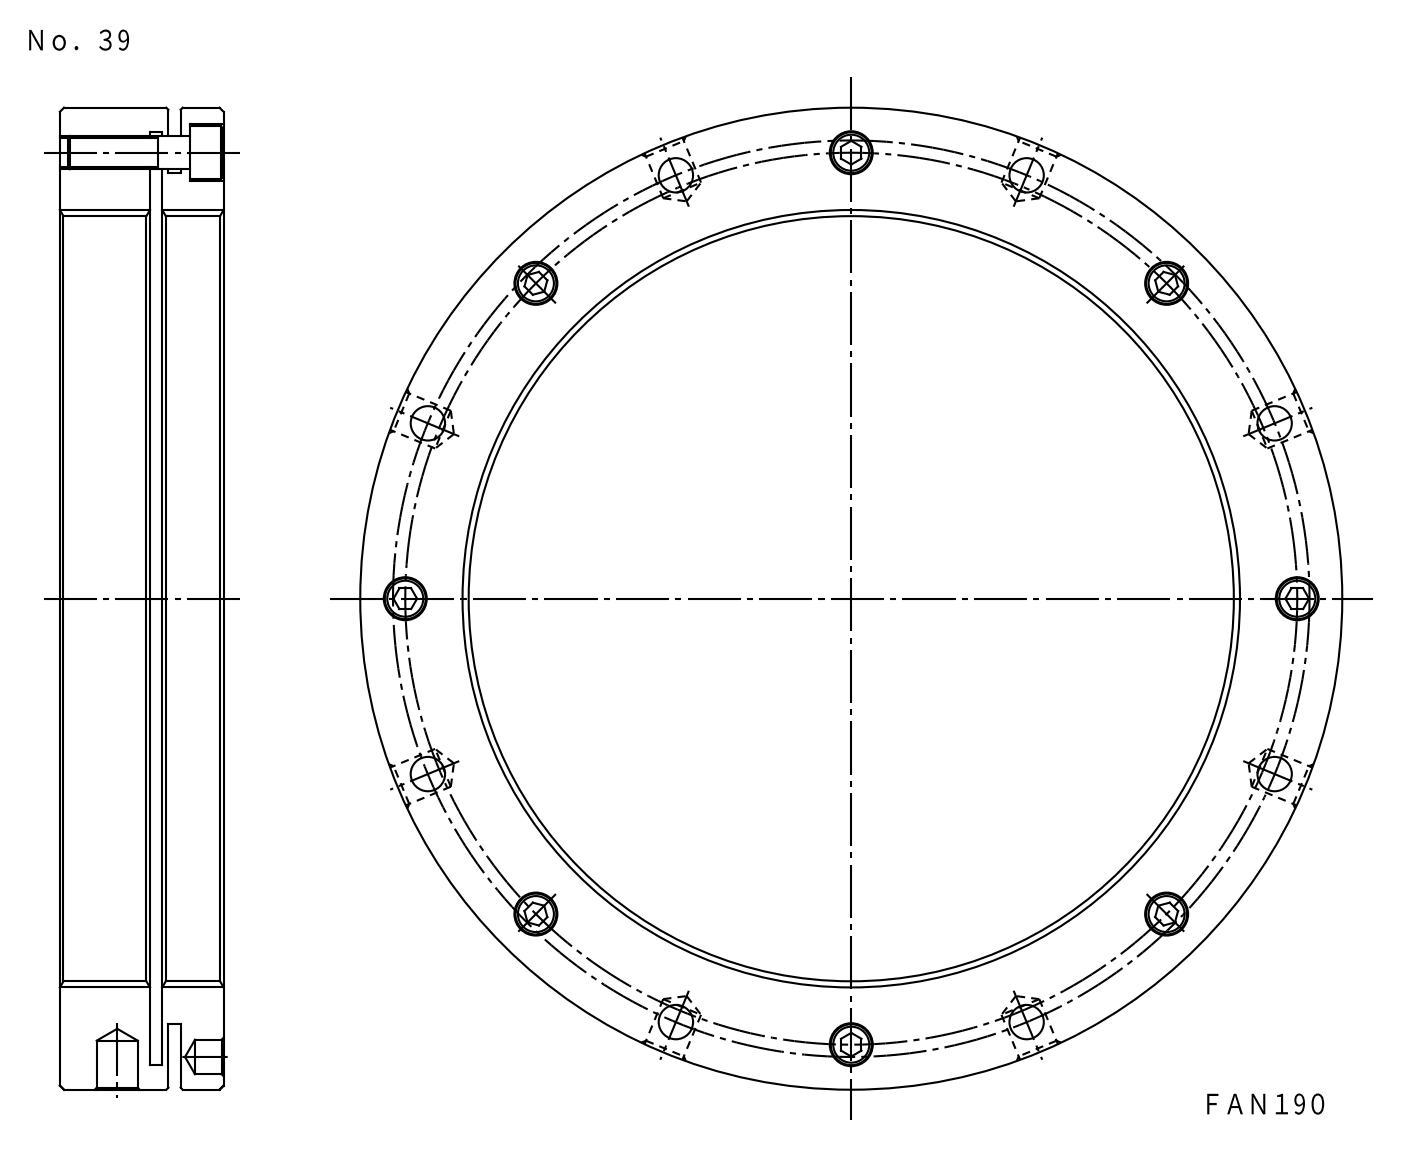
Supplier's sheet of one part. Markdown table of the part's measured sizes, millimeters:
| quantity | value |
| --- | --- |
| part name | FKD FAN190; M8X30_default |
| STEP written by | SolidWorks 2012 (CONFIG_CONTROL_DESIGN) |
| units | millimeters |
| bodies | 9 solids, 266 faces (94 planar, 140 cylindrical, 32 other) |
| overall size | 240 × 240 × 40 |
| volume | 594 275 mm³ |
| surface area | 156 381 mm² |
| round holes (diameter × count) | 8.4 × 8, 8.6 × 8, 10 × 8, 14 × 8, 6.65 × 5, 6.65 × 3, 190 × 1, 228 × 1 |
| round bosses / shafts (diameter × count) | 13 × 8, 8 × 8, 240 × 1, 208 × 1 |
| main face-to-face distances | 3, 4.5, 40, 22, 18, 25, 15, 26.5, 1.5, 13.5 |
| hole center spacings | 122.8, 43.21, 43.22, 83.42, 85.72, 112, 158.39, 183.75 |
